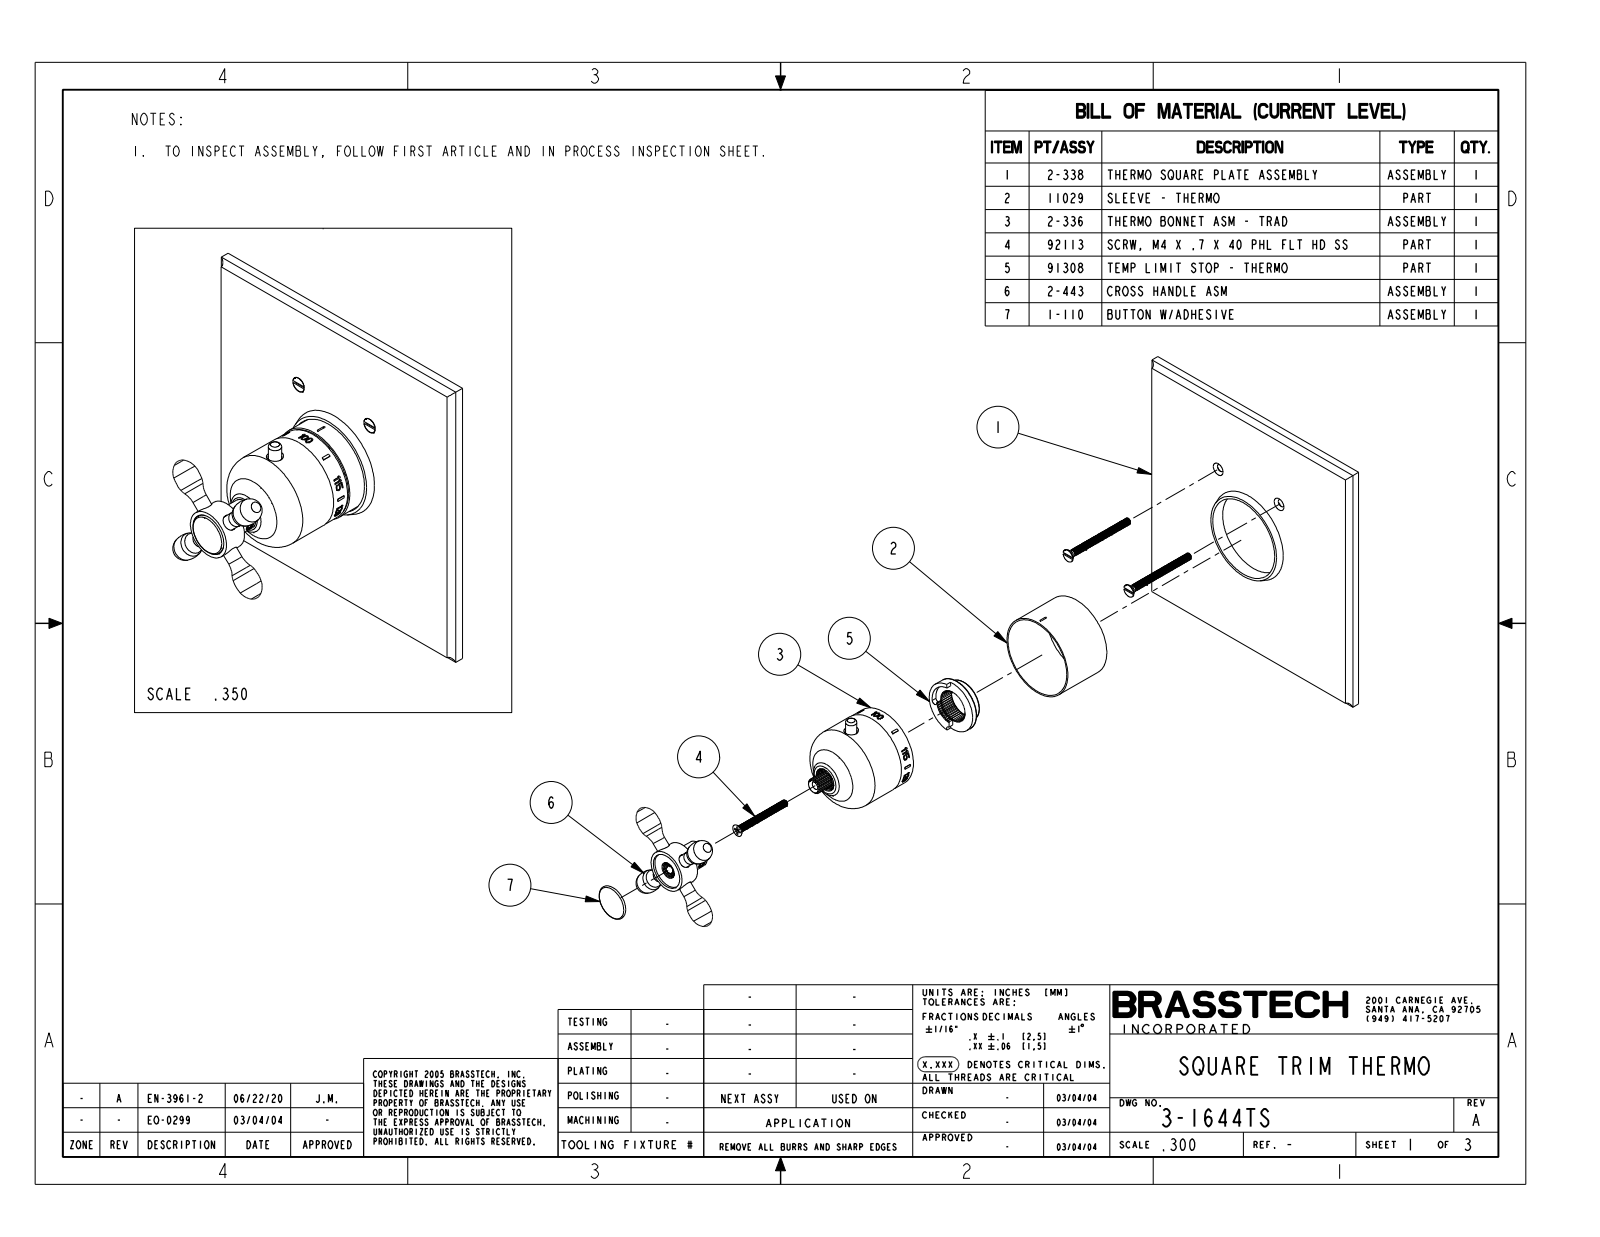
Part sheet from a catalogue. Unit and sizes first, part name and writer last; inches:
Units: inches
Overall size (bounding box): 6.5 × 6.5 × 3.877
Round holes (diameter × count): ⌀0.313 ×1
Round bosses / shafts (diameter × count): ⌀0.3 ×2, ⌀1.97 ×1, ⌀1.94 ×1, ⌀1.929 ×1, ⌀1 ×1, ⌀0.625 ×1, ⌀0.26 ×1, ⌀0.067 ×1
Partial cylindrical surfaces — rounded edges, fillets, slot ends (radius × count): R0.125 ×4, R0.969 ×1
Main face-to-face distances: 0.313, 6.5, 3.756, 3.443, 0.863, 0.55, 2.894, 2.756, 2.443, 1.894
Volume: 20.61 in³ · Surface area: 113.1 in²
Bodies: 1 solid, 440 faces (333 planar, 49 cylindrical, 58 other)
Part name (STEP PRODUCT): 3-1644TS
STEP written by: CREO PARAMETRIC BY PTC INC, 2018400 (CONFIG_CONTROL_DESIGN)
